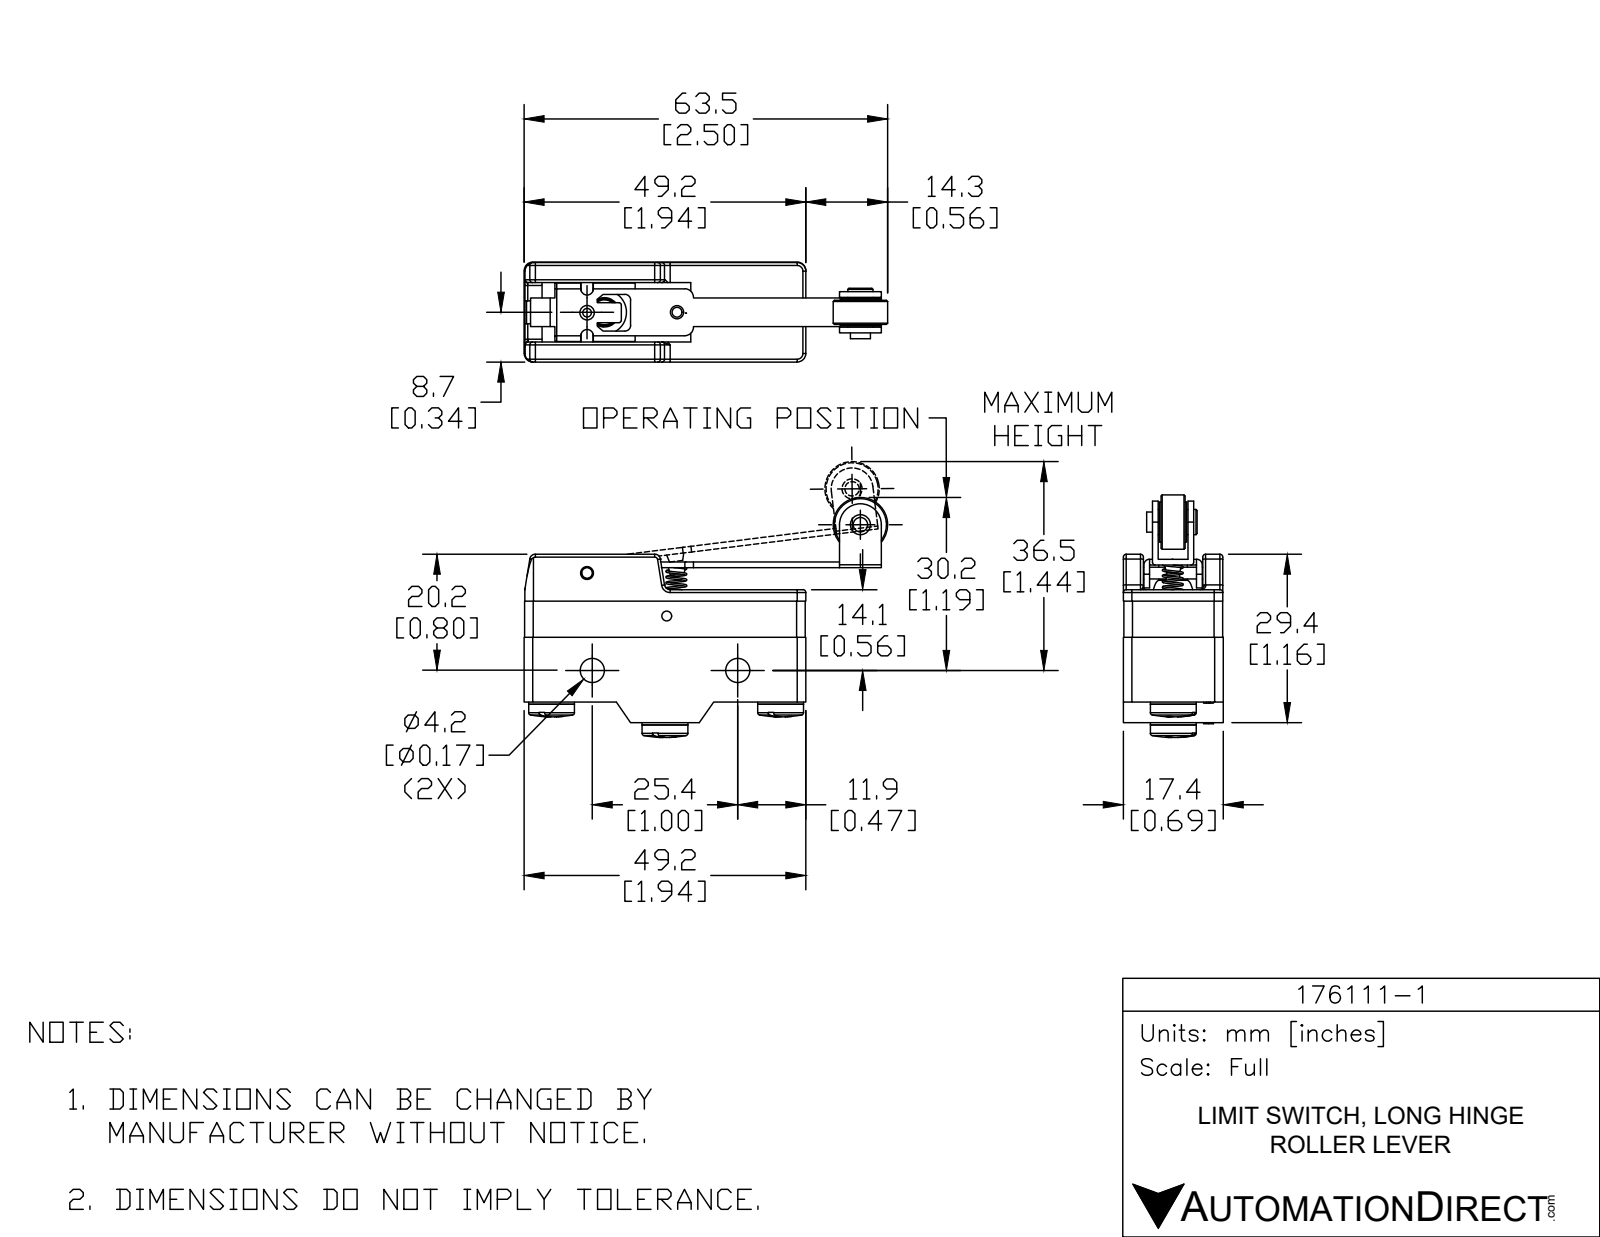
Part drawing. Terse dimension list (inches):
name: 176-MS (Screw Terminal)-Long Hinge Roller Lever
written by: SolidWorks 2018 (AUTOMOTIVE_DESIGN)
unit: in
bodies: 5 solids, 611 faces (287 planar, 131 cylindrical, 193 other)
size: 2.5 × 1.668 × 0.687
volume: 1.103 in³; area: 13.82 in²
holes: 3× ⌀0.236, 2× ⌀0.067, 2× ⌀0.165, 1× ⌀0.079, 1× ⌀0.098, 1× ⌀0.138, 1× ⌀0.173, 1× ⌀0.181, 1× ⌀0.197
bosses: 3× ⌀0.315, 3× ⌀0.15, 1× ⌀0.374, 1× ⌀0.276, 1× ⌀0.081
rounds: 21× R0.02, 13× R0.059, 12× R0.012, 7× R0.039, 3× R0.043, 3× R0.116, 2× R0.016, 2× R0.03
face distances: 0.039, 0.683, 0.687, 0.209, 0.772, 0.137, 0.941, 0.17, 0.981, 0.546
hole spacings: 0.076, 0.082, 0.363, 0.416, 0.492, 0.498, 0.615, 0.622
